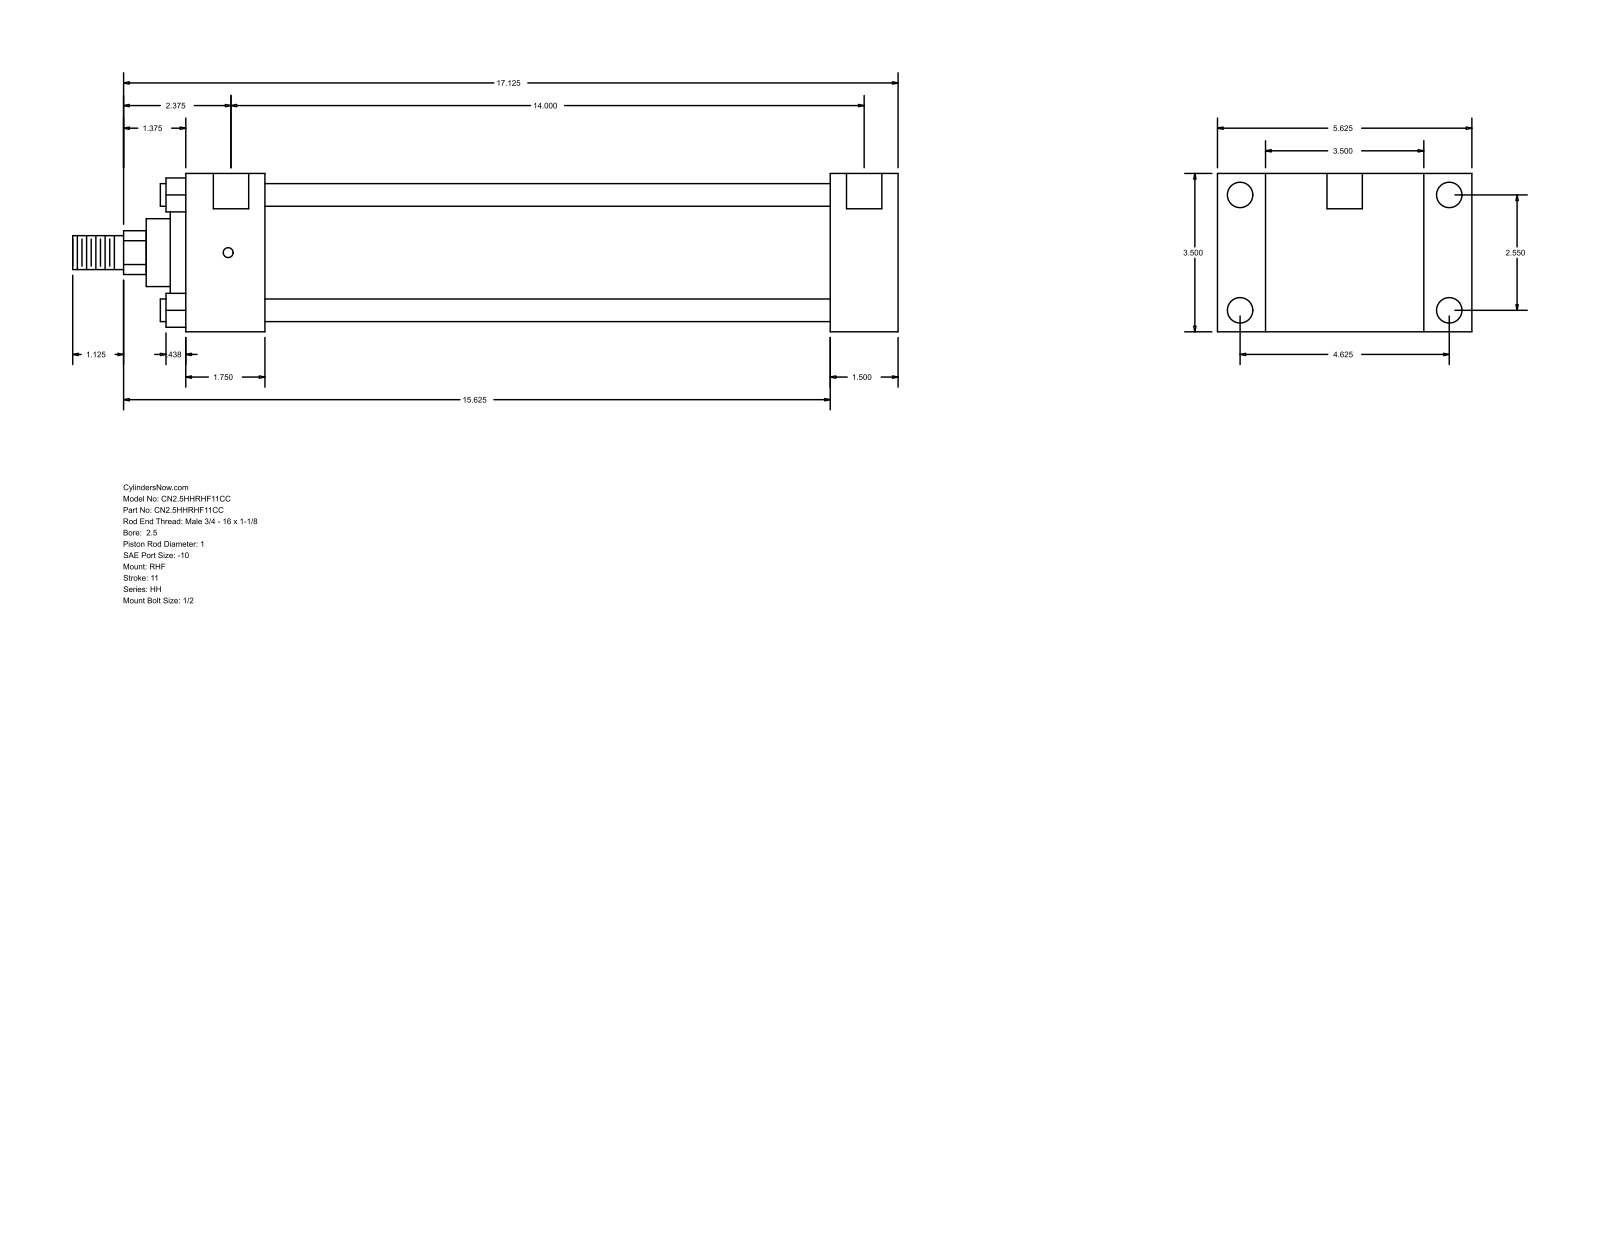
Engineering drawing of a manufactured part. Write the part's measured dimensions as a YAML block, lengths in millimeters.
part_name: "HH_RHF__0250_1"
step_written_by: "GSSL Pune (CONFIG_CONTROL_DESIGN)"
units: millimeters
bodies: {solids: 0, faces: 90, planar: 61, cylindrical: 29, other: 0}
overall_size: [463.55, 142.88, 88.9]
round_holes:
  - {diameter: 5.56, count: 4}
  - {diameter: 14.3, count: 4}
  - {diameter: 19.84, count: 2}
round_bosses_or_shafts:
  - {diameter: 12.7, count: 4}
  - {diameter: 73.03, count: 1}
  - {diameter: 60.33, count: 1}
  - {diameter: 38.1, count: 1}
  - {diameter: 25.4, count: 1}
  - {diameter: 19.05, count: 1}
partial_cylinders:
  - {radius: 12.29, count: 1}
face_to_face_distances: [88.9, 38.1, 26.99, 115.89, 361.96, 400.06, 142.88, 44.46, 317.5, 355.6]
hole_center_spacings: [64.76, 117.48, 134.15, 358.77, 1.58, 1.59, 355.6, 357.18]
